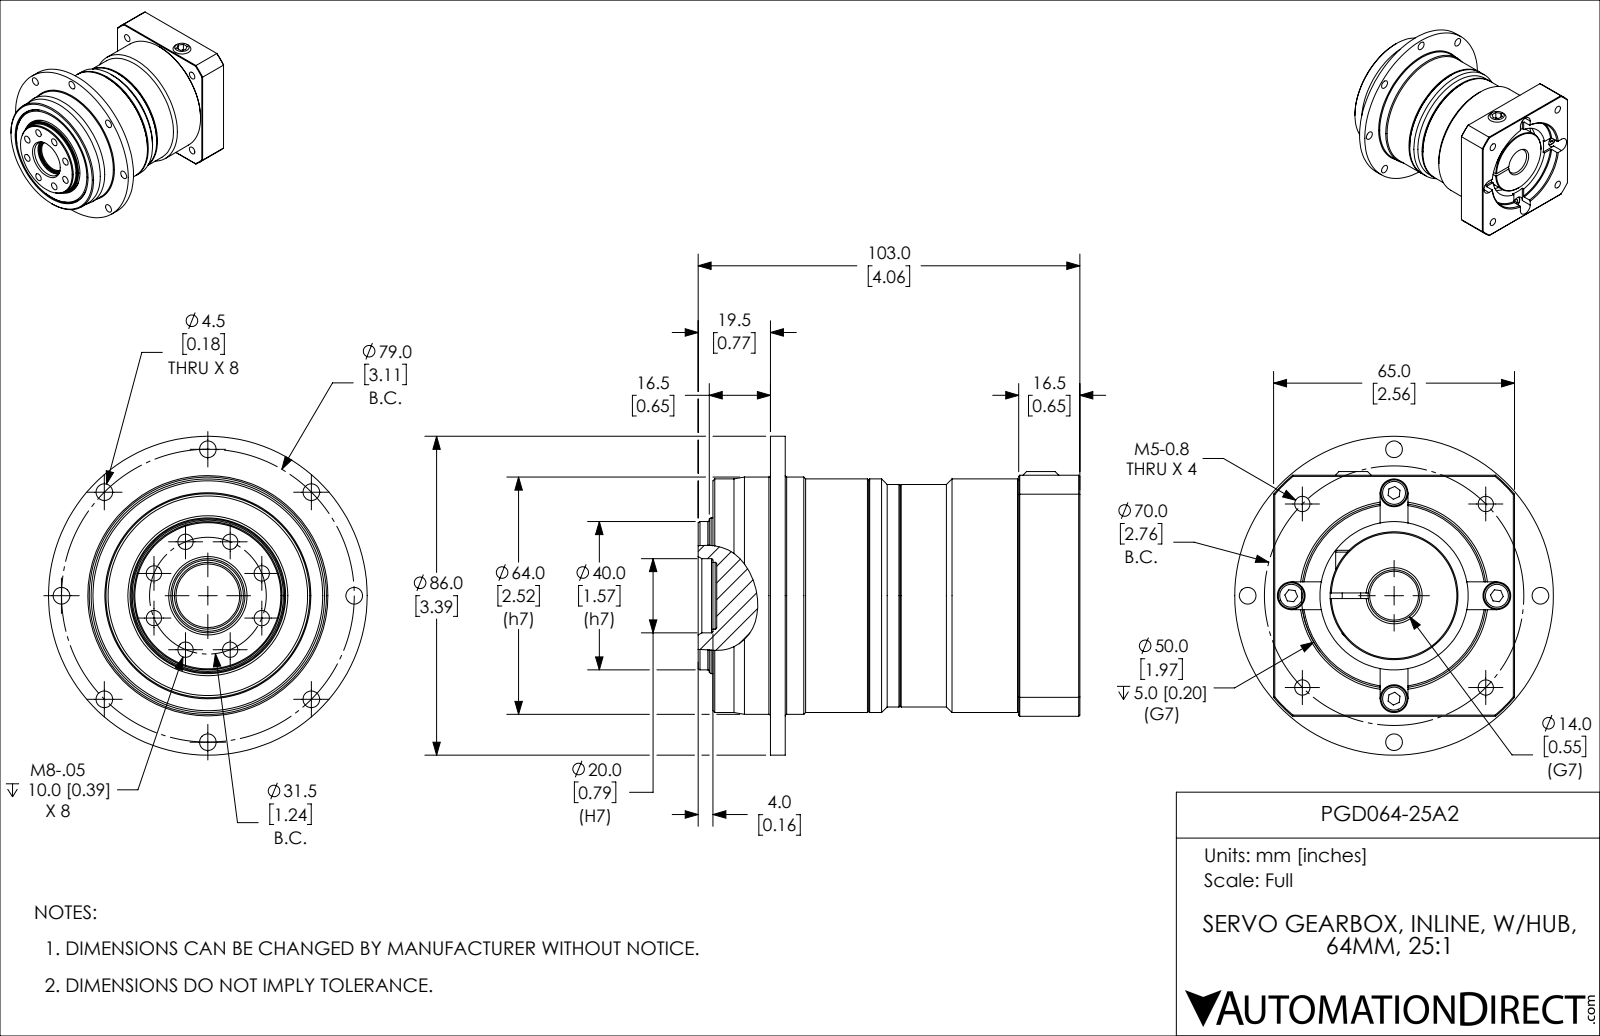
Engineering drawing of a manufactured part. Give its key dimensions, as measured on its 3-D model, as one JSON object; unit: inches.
{"part_name": "PGD064-25A2", "step_written_by": "SolidWorks 2015 (AUTOMOTIVE_DESIGN)", "units": "inches", "bodies": {"solids": 10, "faces": 388, "planar": 131, "cylindrical": 160, "other": 97}, "overall_size": [4.055, 3.386, 3.386], "volume_in3": 18.81, "surface_area_in2": 74.7, "round_holes": [[0.163, 12], [0.177, 9], [0.295, 4], [0.197, 2], [0.128, 1], [0.157, 1], [0.315, 1], [0.551, 1], [0.709, 1], [0.787, 1], [1.575, 1], [1.969, 1]], "round_bosses_or_shafts": [[3.386, 1], [2.52, 1], [2.48, 1], [2.362, 1], [1.654, 1], [1.142, 1], [0.276, 1], [0.157, 1]], "partial_cylinders_radius": [[1.673, 1]], "face_to_face_distances": [0.157, 3.287, 0.906, 3.13, 0.65, 2.559, 0.748, 4.035, 0.768, 0.098], "hole_center_spacings": [1.437, 2.141, 0.62, 0.571, 0.839, 0.877, 0.981, 1.01]}
